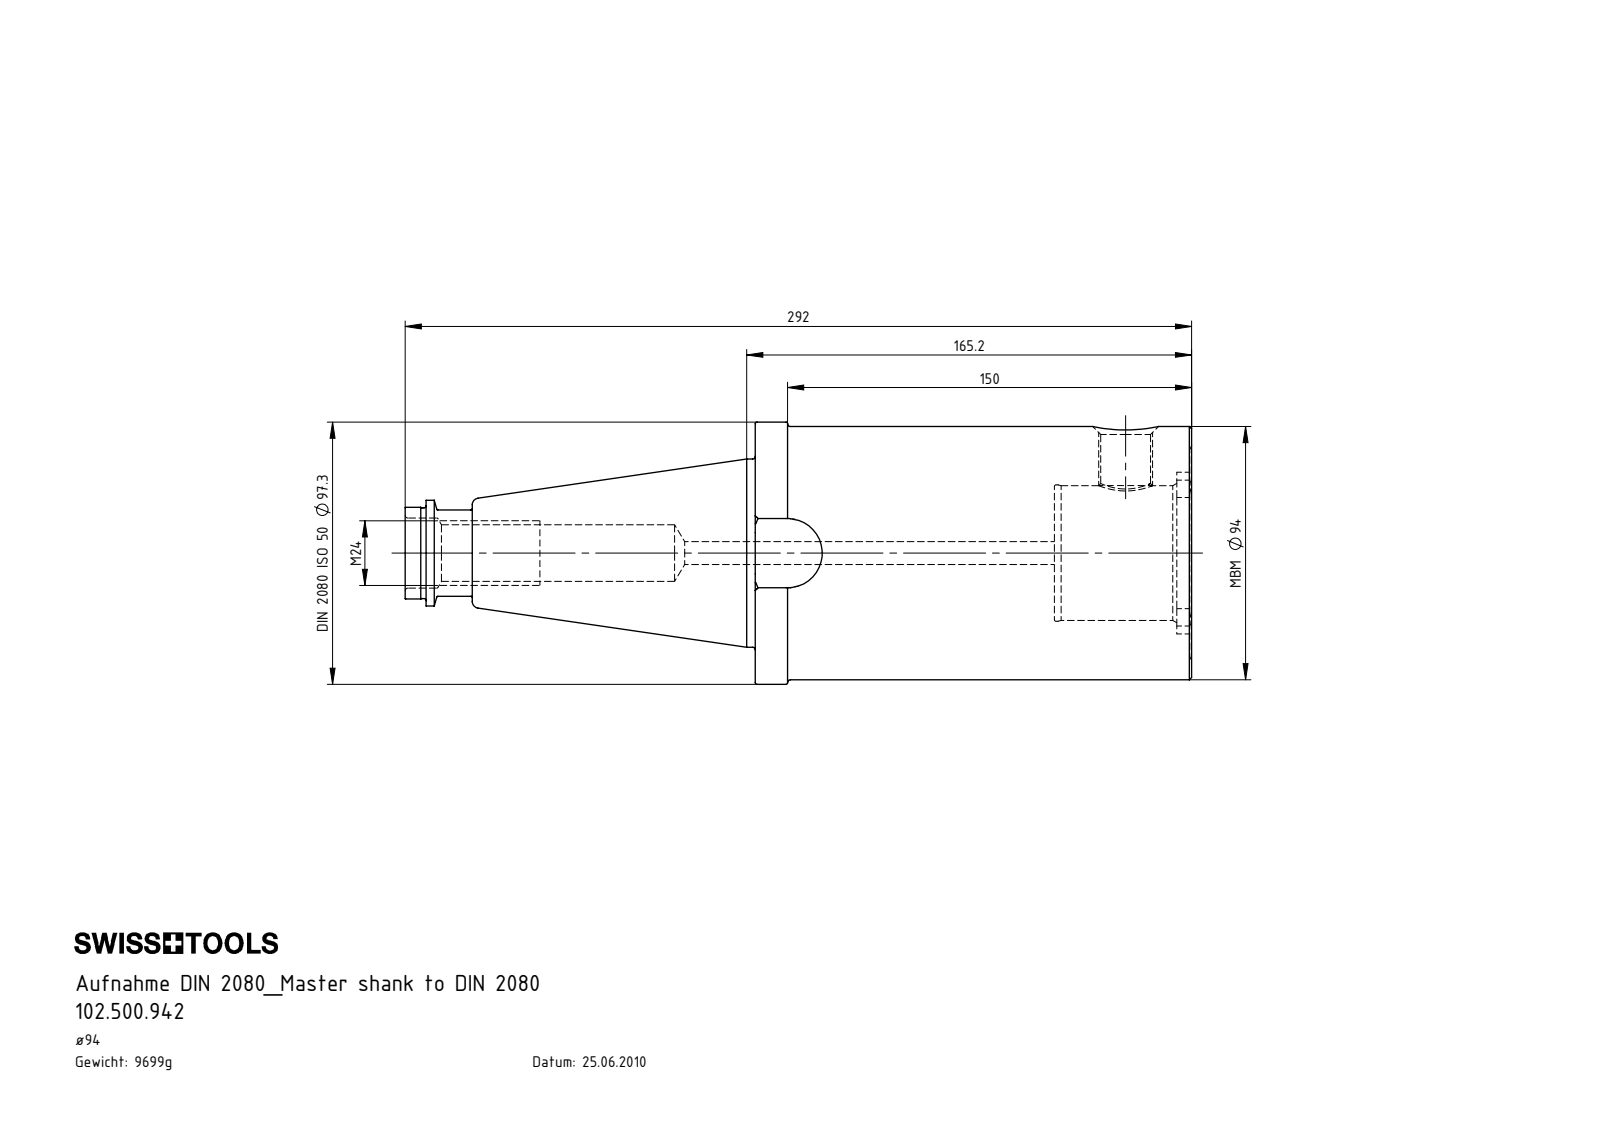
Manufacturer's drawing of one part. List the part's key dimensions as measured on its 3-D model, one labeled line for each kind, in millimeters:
Part name (STEP PRODUCT): MB9-ER1.001.032_B; 102.500.942; SZ5-MB9.K01.165_C
STEP written by: SolidWorks 2017 (CONFIG_CONTROL_DESIGN)
Units: millimetres
Bodies: 2 solids, 150 faces (38 planar, 51 cylindrical, 61 other)
Overall size (bounding box): 292 × 97.3 × 94
Volume: 1 243 000 mm³ · Surface area: 103 834 mm²
Round holes (diameter × count): ⌀8.5 ×1, ⌀18.5 ×1, ⌀21 ×1, ⌀26 ×1, ⌀50 ×1, ⌀50.6 ×1
Round bosses / shafts (diameter × count): ⌀97.3 ×1, ⌀94 ×1, ⌀69.85 ×1, ⌀39.24 ×1, ⌀34.05 ×1, ⌀33.65 ×1, ⌀32 ×1, ⌀20 ×1
Partial cylindrical surfaces — rounded edges, fillets, slot ends (radius × count): R2 ×8, R5.2 ×4, R12.85 ×1, R30 ×1, R37.52 ×1
Main face-to-face distances: 111, 156.45, 45.45, 162, 51, 5.55, 161.25, 50.25, 4.8, 0.75
